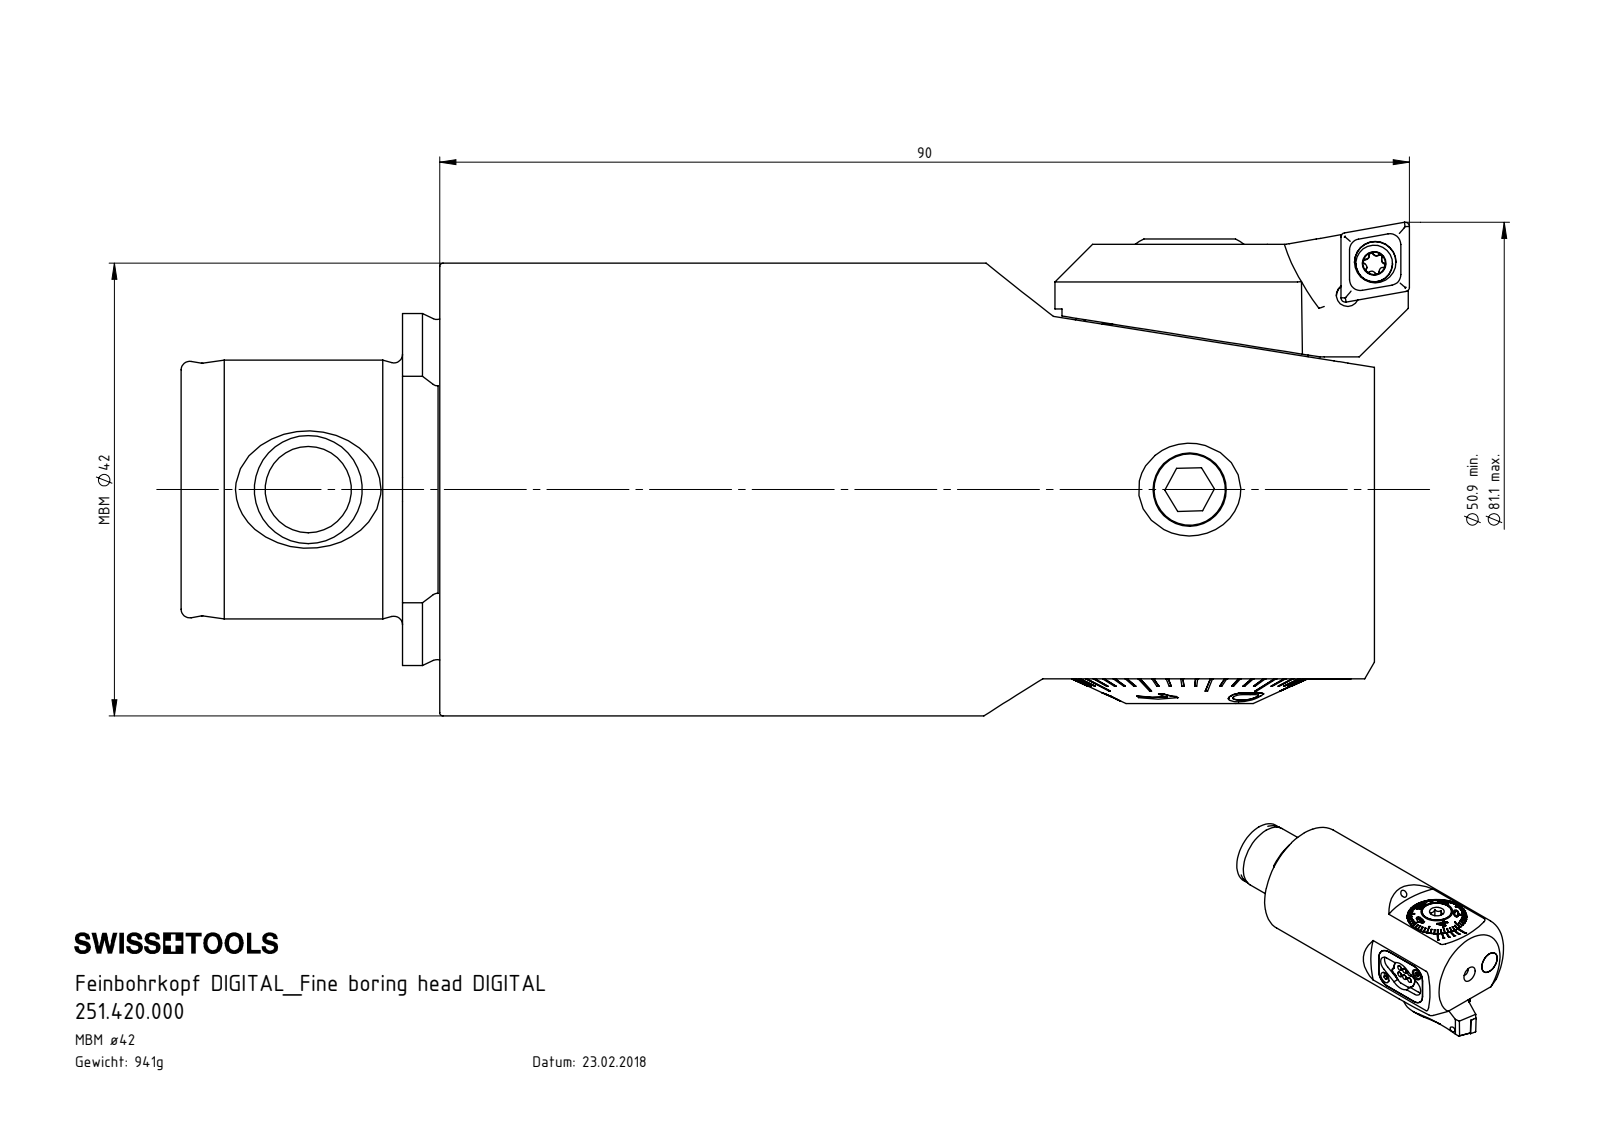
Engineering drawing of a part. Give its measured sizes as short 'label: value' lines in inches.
name: A42-BG2.013.005_B; Fxx-MAB.xxx.xxx_A_F42; 251.420.000; A42-BG1.012.006_B (+8 more)
written by: SolidWorks 2017 (CONFIG_CONTROL_DESIGN)
unit: in
bodies: 24 solids, 1016 faces (441 planar, 233 cylindrical, 342 other)
size: 4.488 × 1.803 × 1.654
volume: 7.42 in³; area: 55.09 in²
holes: 4× ⌀0.13, 2× ⌀0.063, 2× ⌀0.087, 2× ⌀0.098, 2× ⌀0.165, 2× ⌀0.268, 2× ⌀0.315, 2× ⌀0.335, 1× ⌀0.081, 1× ⌀0.083, 1× ⌀0.11, 1× ⌀0.118
bosses: 6× ⌀0.075, 2× ⌀0.315, 2× ⌀0.15, 2× ⌀0.079, 1× ⌀1.654, 1× ⌀0.945, 1× ⌀0.865, 1× ⌀0.862
rounds: 8× R0.047, 6× R0.008, 6× R0.043, 5× R0.014, 5× R0.02, 5× R0.126, 4× R0.177, 3× R0.173
face distances: 0.177, 1.091, 0.157, 0.043, 0.22, 1.366, 0.091, 0.079, 0.13, 0.087
hole spacings: 0.375, 0.151, 0.157, 0.302, 0.413, 0.613, 0.75, 1.215
